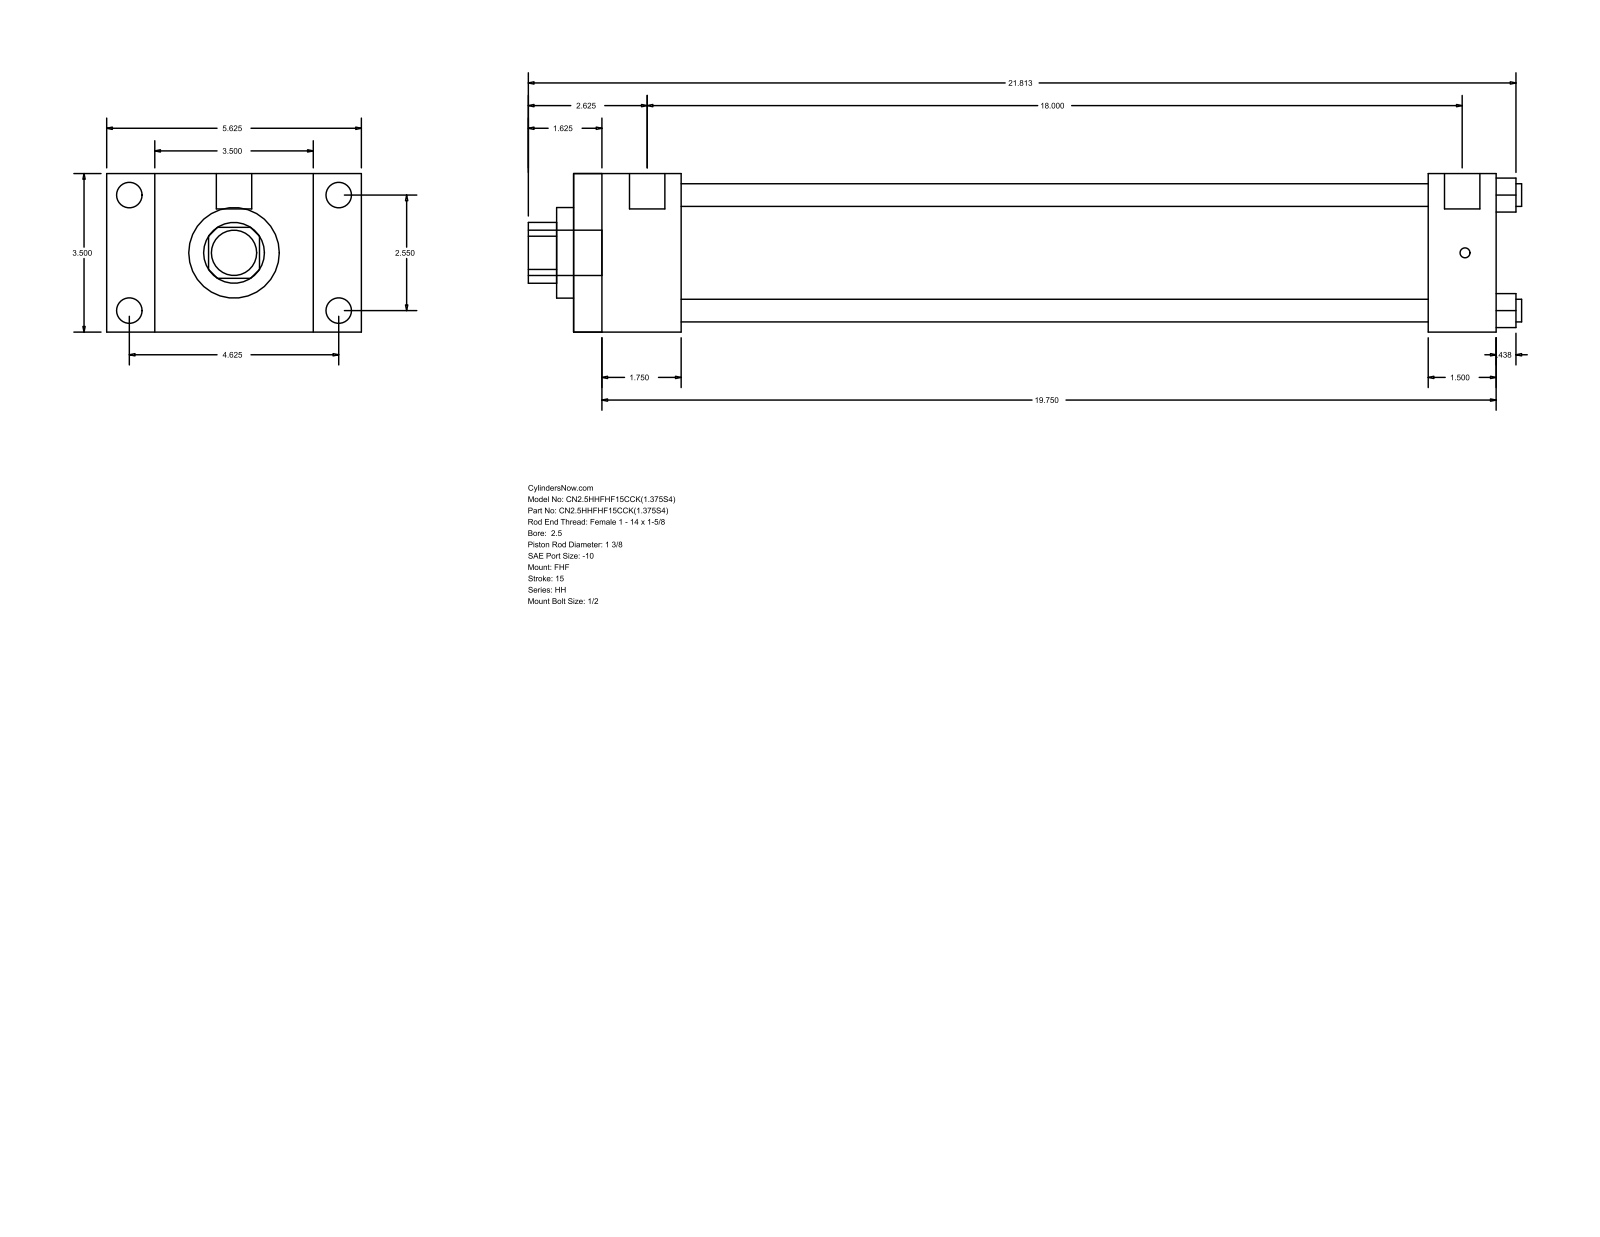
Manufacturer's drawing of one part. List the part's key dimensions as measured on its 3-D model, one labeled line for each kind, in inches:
Part name (STEP PRODUCT): HH_FHF__0250_1.375
STEP written by: GSSL Pune (CONFIG_CONTROL_DESIGN)
Units: inches
Bodies: 0 solids, 88 faces (60 planar, 28 cylindrical, 0 other)
Overall size (bounding box): 21.937 × 5.625 × 3.5
Round holes (diameter × count): ⌀0.5 ×4, ⌀1.375 ×1, ⌀2 ×1, ⌀2.875 ×1
Round bosses / shafts (diameter × count): ⌀0.563 ×4, ⌀0.219 ×4, ⌀0.781 ×2, ⌀1 ×1
Partial cylindrical surfaces — rounded edges, fillets, slot ends (radius × count): R0.672 ×1
Main face-to-face distances: 3.5, 2.375, 1.063, 4.563, 20.375, 18, 5.625, 18.875, 16.5, 1.5
Hole centre spacings: 1.803, 2.55, 3.606
